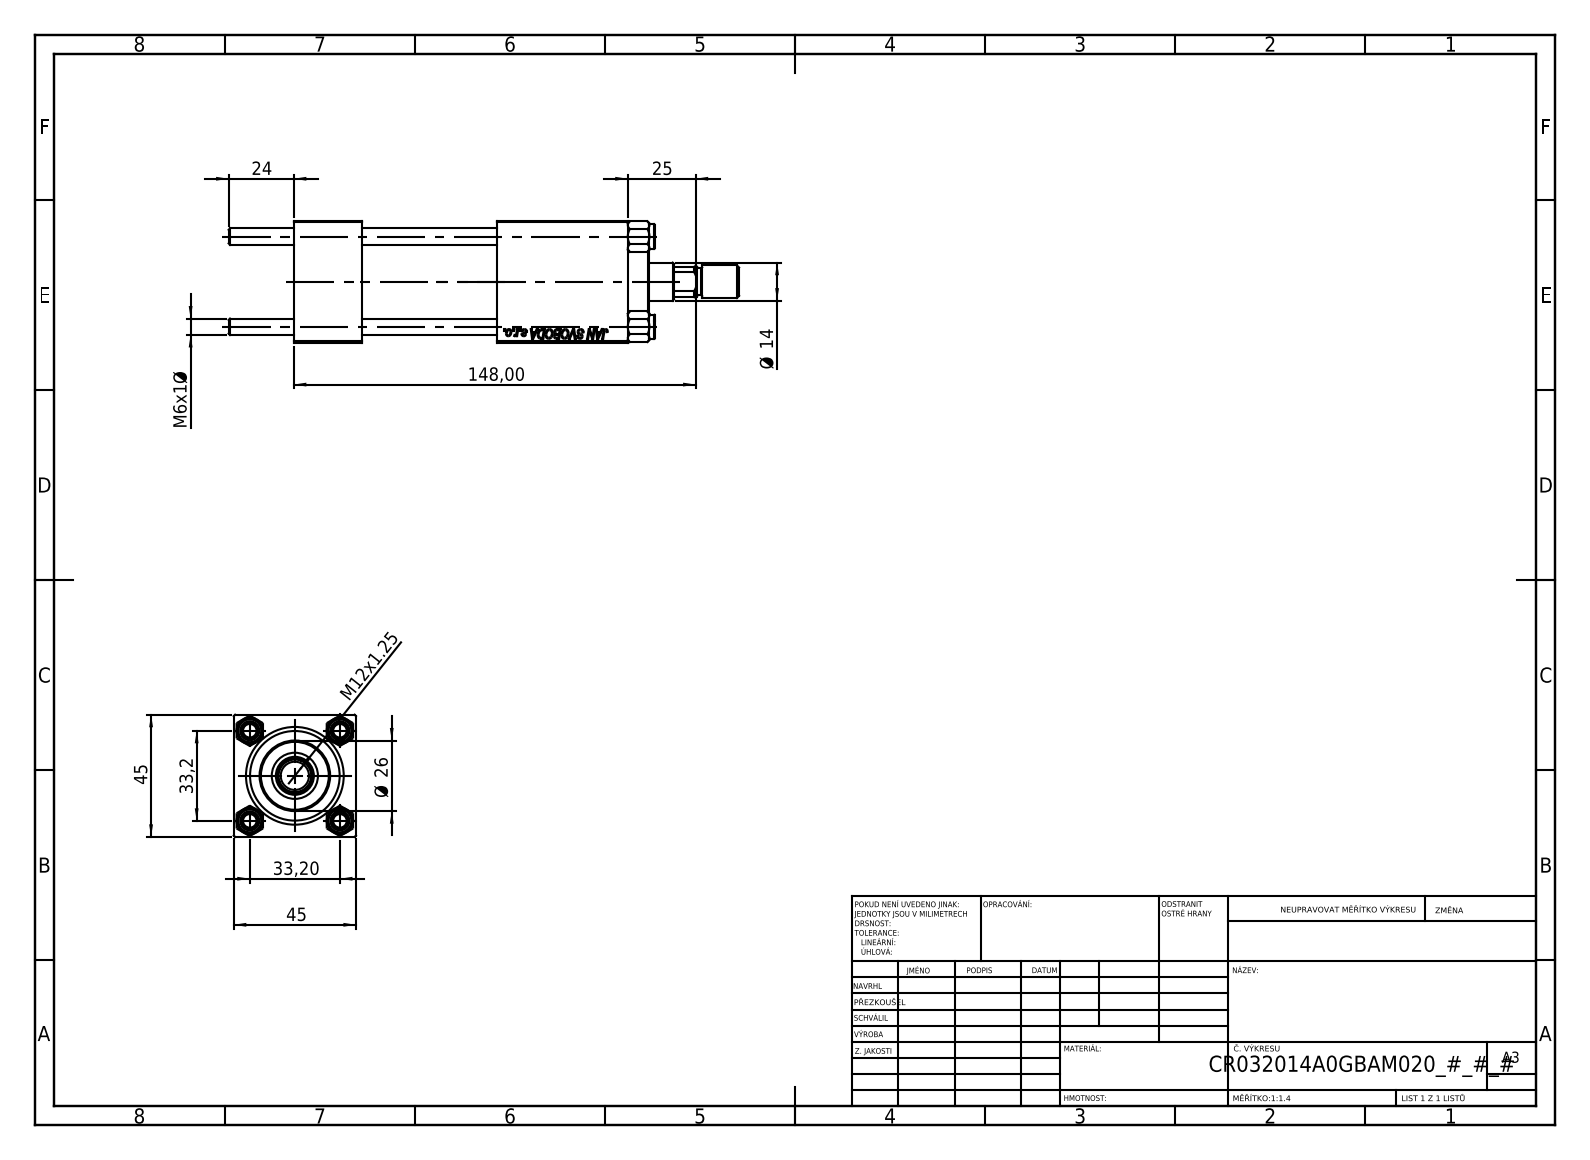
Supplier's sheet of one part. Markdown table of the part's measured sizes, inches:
| quantity | value |
| --- | --- |
| part name | V215CR_VCP; V215_VC_A; ROD_END_AH; NUT_M5 (+2 more) |
| STEP written by | SolidWorks 2019 (CONFIG_CONTROL_DESIGN) |
| units | inches |
| bodies | 12 solids, 1145 faces (521 planar, 82 cylindrical, 542 other) |
| overall size | 7.402 × 1.772 × 1.772 |
| volume | 12.22 in³ |
| surface area | 114.1 in² |
| round holes (diameter × count) | 0.236 × 4, 0.276 × 2, 0.518 × 2, 0.787 × 2, 0.256 × 1, 0.551 × 1, 0.669 × 1, 0.945 × 1, 1.26 × 1, 1.299 × 1 |
| round bosses / shafts (diameter × count) | 0.354 × 4, 1.496 × 1, 1.024 × 1, 0.472 × 1, 0.394 × 1 |
| partial cylindrical surfaces (radius × count) | 0.256 × 1 |
| main face-to-face distances | 1.772, 0.984, 4.843, 3.858, 1.969, 2.953, 1.89, 3.713, 2.728, 0.76 |
| hole center spacings | 0.924, 1.307, 1.848, 2.972 |
